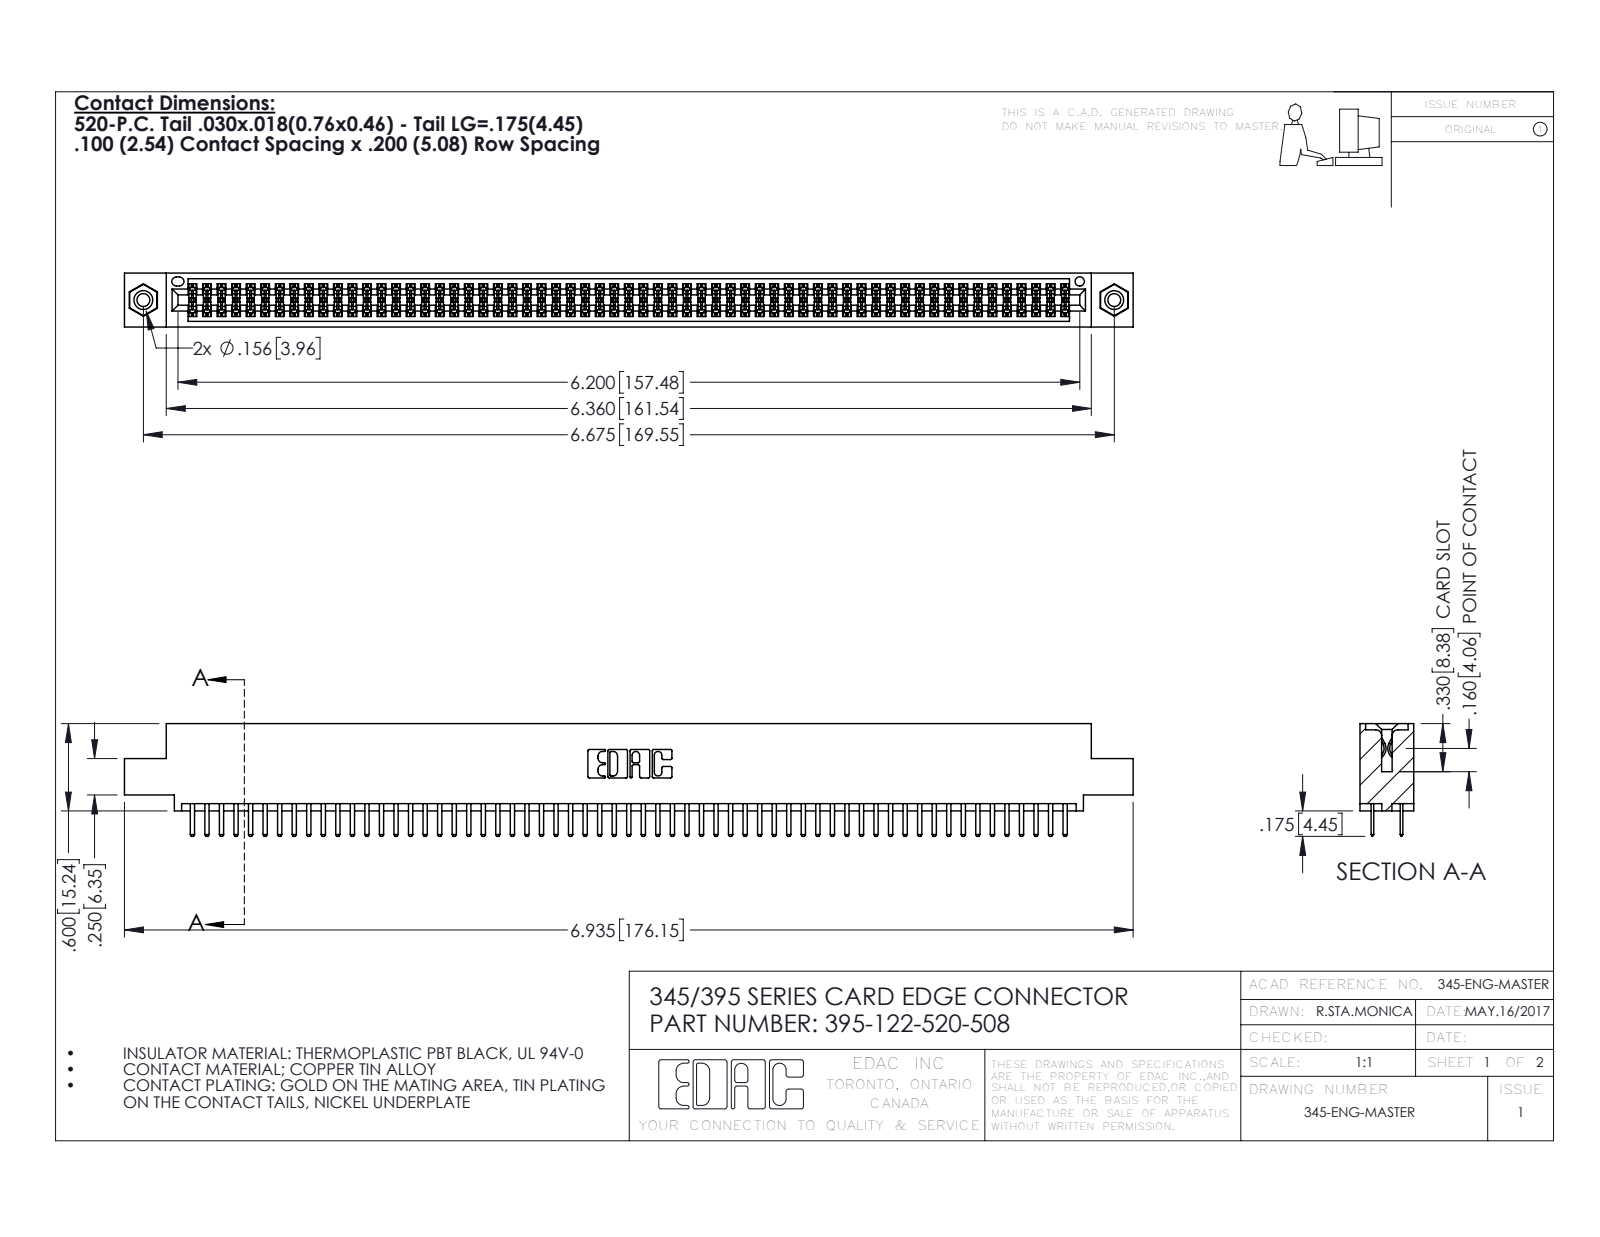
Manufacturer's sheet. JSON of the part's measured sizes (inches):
{"part_name": "345 Part_0.110 Offset - 0.156 Dia-TI; 345-250-001_345-250-003-102; 395-122-520-508; 345-292-001_345-293-120", "step_written_by": "SolidWorks 2016 (CONFIG_CONTROL_DESIGN)", "units": "inches", "bodies": {"solids": 125, "faces": 6778, "planar": 4386, "cylindrical": 2376, "other": 16}, "overall_size": [6.935, 0.775, 0.37], "volume_in3": 1.047, "surface_area_in2": 39.86, "round_holes": [[0.089, 2], [0.125, 2], [0.156, 2], [0.064, 1]], "round_bosses_or_shafts": [[0.155, 2]], "partial_cylinders_radius": [[0.006, 183], [0.01, 126], [0.01, 22], [0.007, 6], [0.031, 6], [0.026, 3], [0.014, 2], [0.019, 2]], "face_to_face_distances": [0.072, 0.298, 0.2, 0.37, 0.098, 0.272, 0.025, 0.225, 0.022, 0.072], "hole_center_spacings": [0.27, 6.439, 6.675]}
